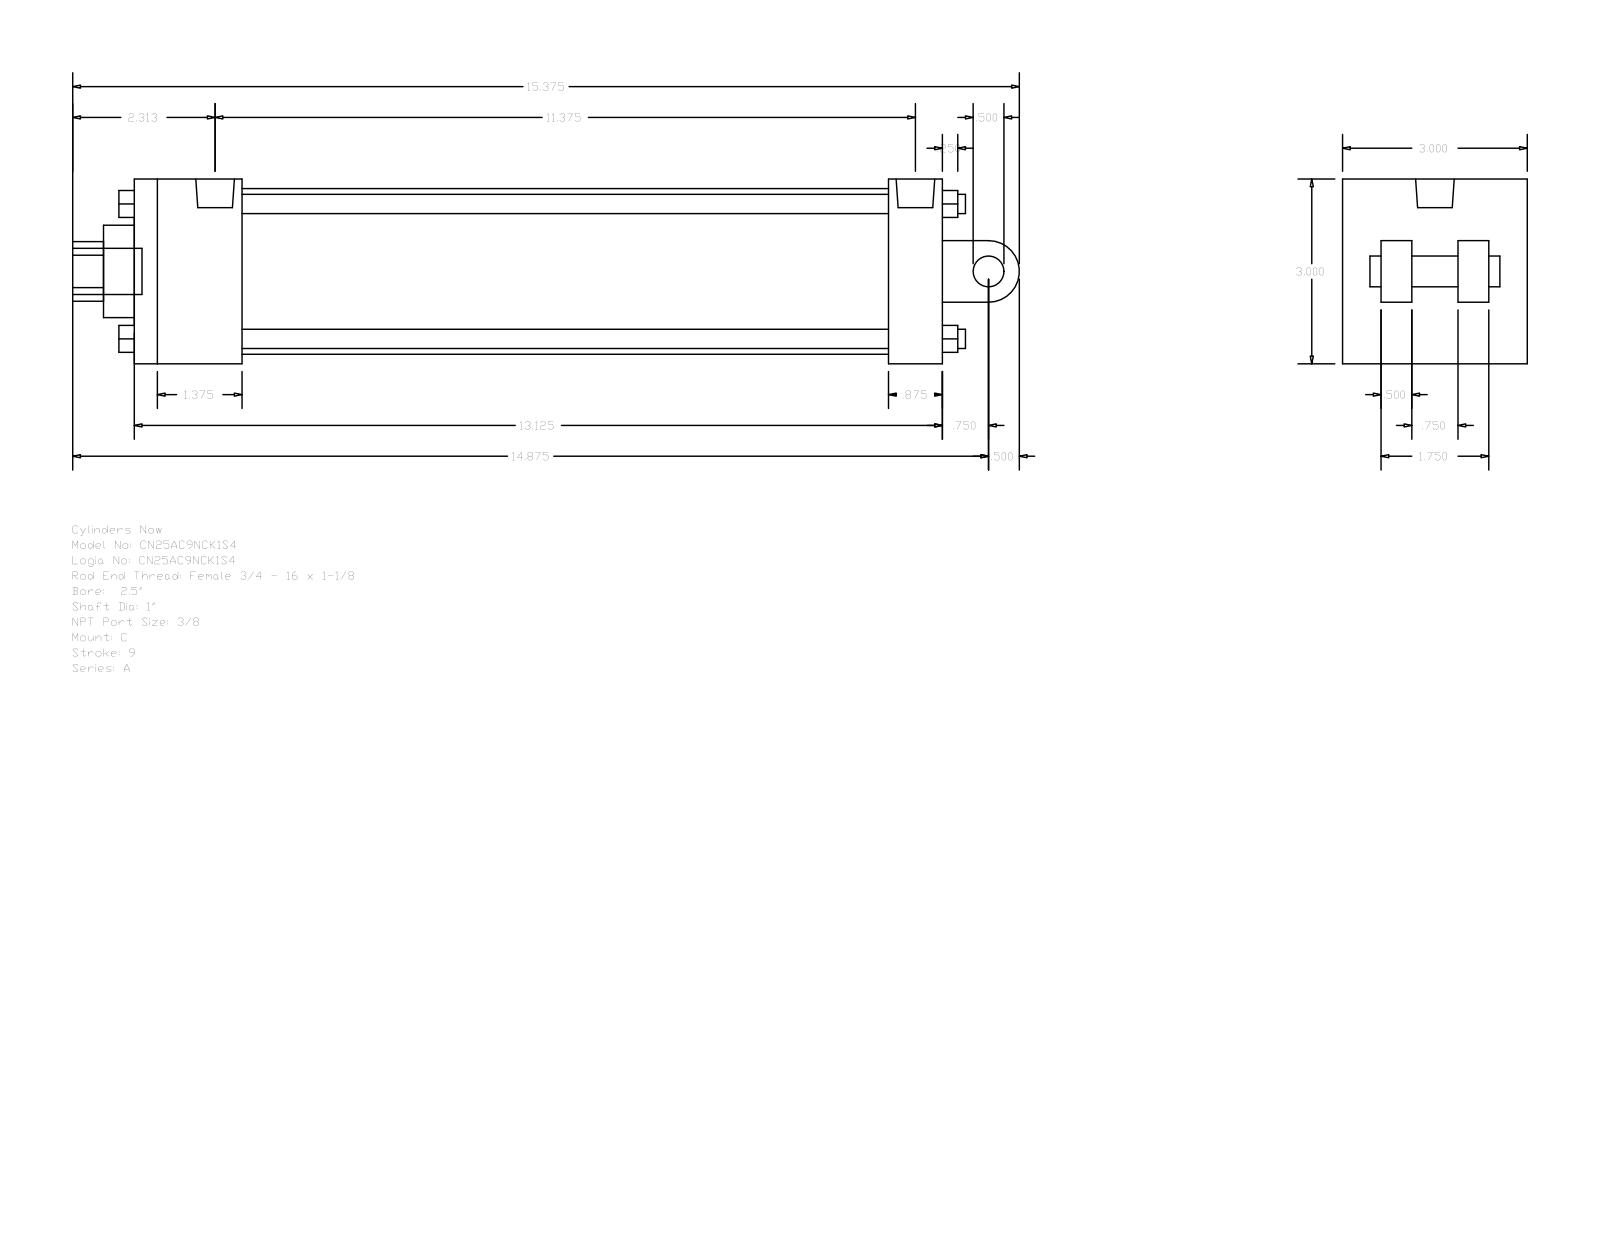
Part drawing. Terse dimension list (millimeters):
name: A_C__0250_1
written by: GSSL Pune (CONFIG_CONTROL_DESIGN)
unit: mm
bodies: 0 solids, 135 faces (102 planar, 33 cylindrical, 0 other)
size: 390.52 × 76.2 × 76.2
holes: 2× ⌀5.56, 1× ⌀15.93, 1× ⌀25.4, 1× ⌀38.1, 1× ⌀68.33
bosses: 4× ⌀7.94, 2× ⌀5.56, 1× ⌀19.05, 1× ⌀15.93, 1× ⌀12.7
rounds: 1× R12.29, 1× R12.7
face distances: 76.2, 333.37, 12.7, 44.45, 311.15, 266.7, 288.92, 22.22, 15.87, 25.4
hole spacings: 2.38
